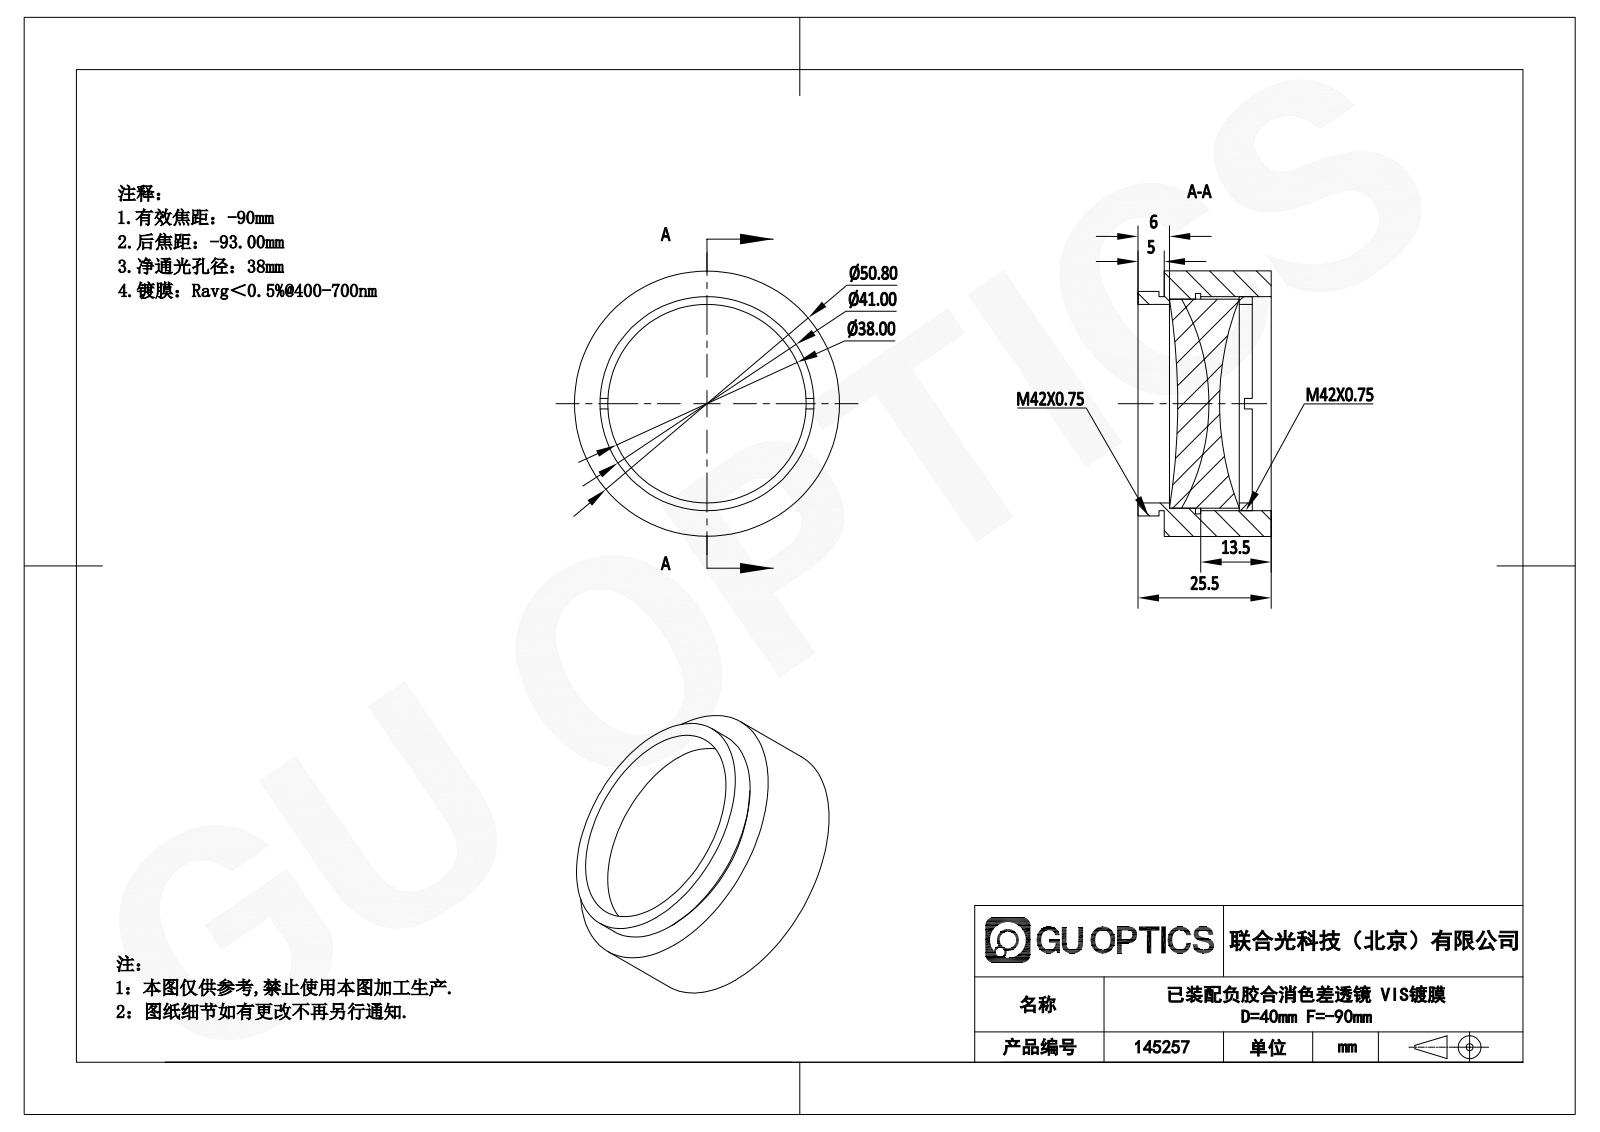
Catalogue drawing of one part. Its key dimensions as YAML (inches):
part_name: "145257"
step_written_by: "SolidWorks 2020 (CONFIG_CONTROL_DESIGN)"
units: inches
bodies: {solids: 4, faces: 46, planar: 16, cylindrical: 22, other: 8}
overall_size: [2, 2, 1.004]
volume: 1.845
surface_area: 26.79
round_holes:
  - {diameter: 1.496, count: 1}
  - {diameter: 1.661, count: 1}
round_bosses_or_shafts:
  - {diameter: 2, count: 1}
  - {diameter: 1.693, count: 1}
  - {diameter: 1.614, count: 1}
  - {diameter: 1.575, count: 1}
face_to_face_distances: [0.807, 0.197, 0.236, 0.039, 1.004, 0.276, 0.566, 0.763, 0.241, 0.861]
